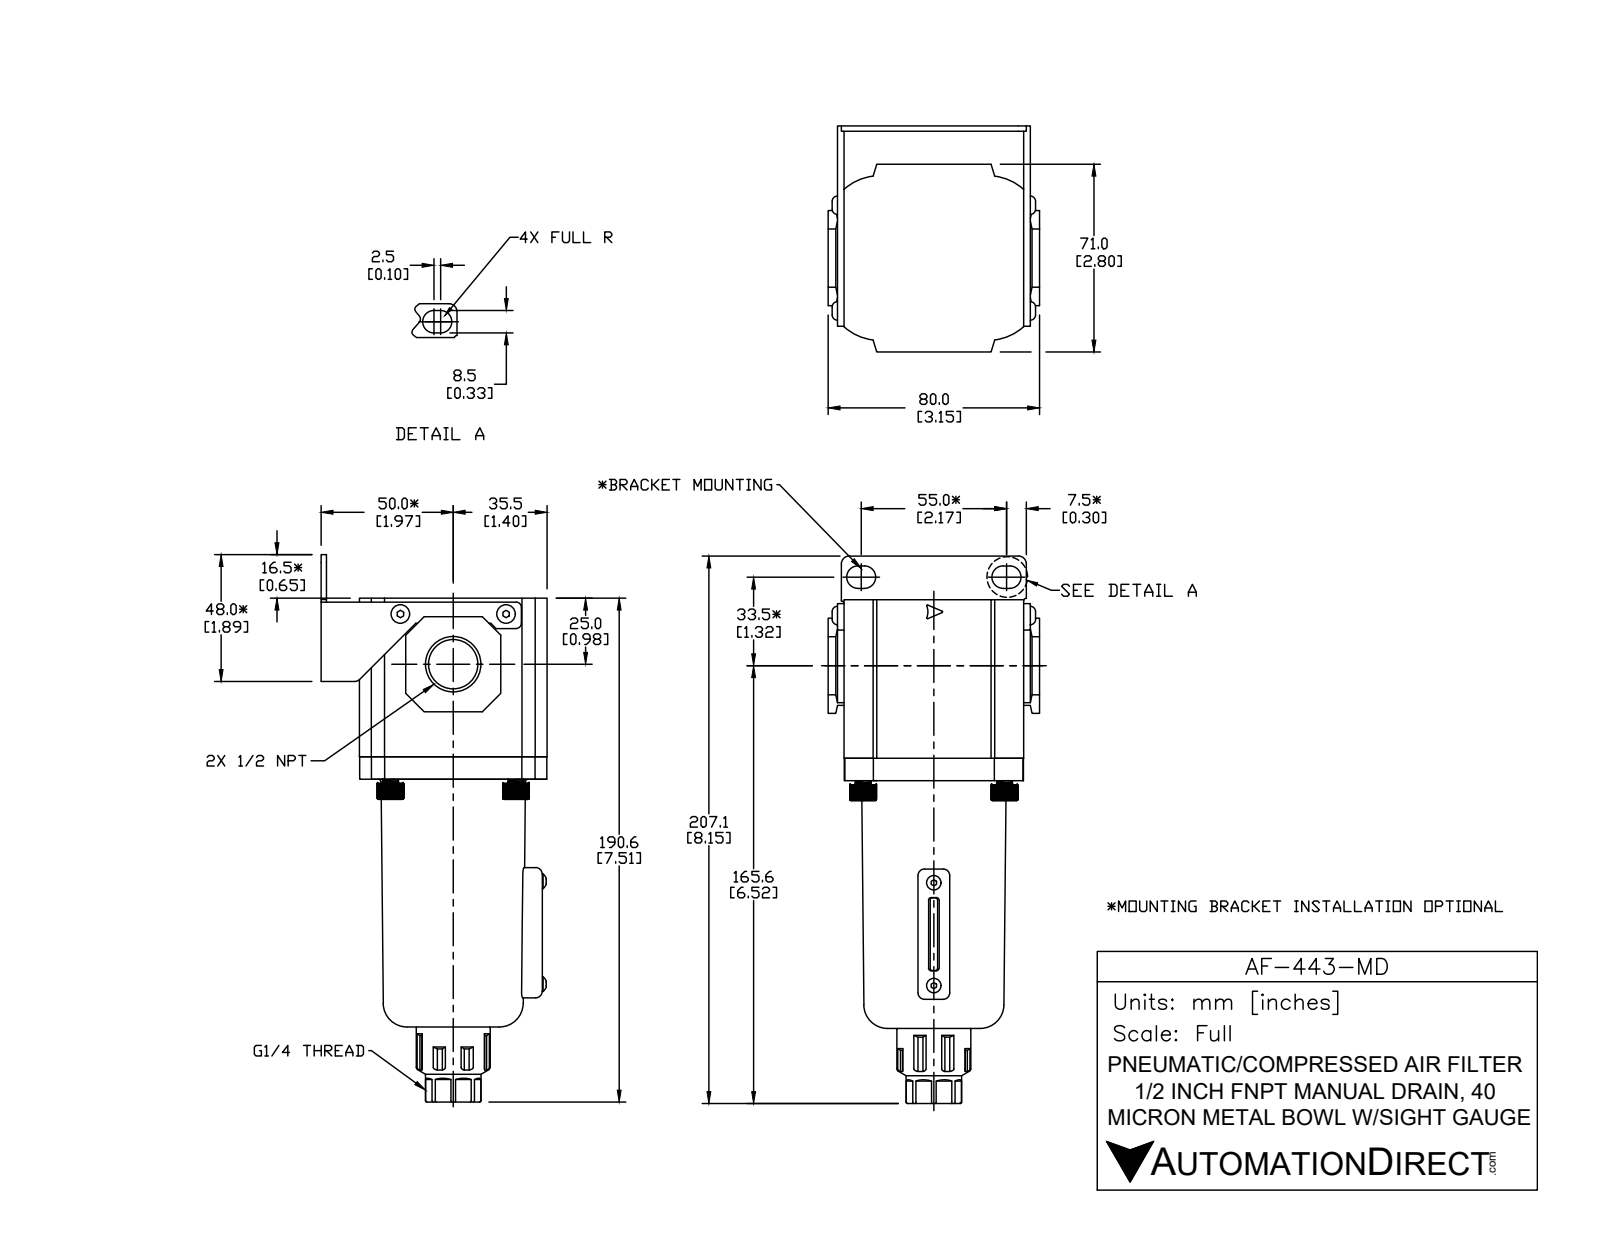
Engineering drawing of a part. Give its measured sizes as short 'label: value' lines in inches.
name: AF-443-MD
written by: SolidWorks 2015 (CONFIG_CONTROL_DESIGN)
unit: in
bodies: 9 solids, 416 faces (245 planar, 98 cylindrical, 73 other)
size: 8.155 × 3.374 × 3.15
volume: 33.52 in³; area: 119 in²
holes: 2× ⌀0.134, 1× ⌀0.244, 1× ⌀0.703
bosses: 4× ⌀0.394, 2× ⌀0.217, 1× ⌀1.102, 1× ⌀0.827
rounds: 8× R0.051, 8× R0.098, 8× R0.374, 6× R0.02, 5× R0.079, 4× R0.012, 4× R0.039, 4× R0.167
face distances: 0.098, 2.362, 2.677, 0.571, 0.472, 2.776, 2.795, 3.366, 3.268, 0.335
hole spacings: 1.086, 1.575
